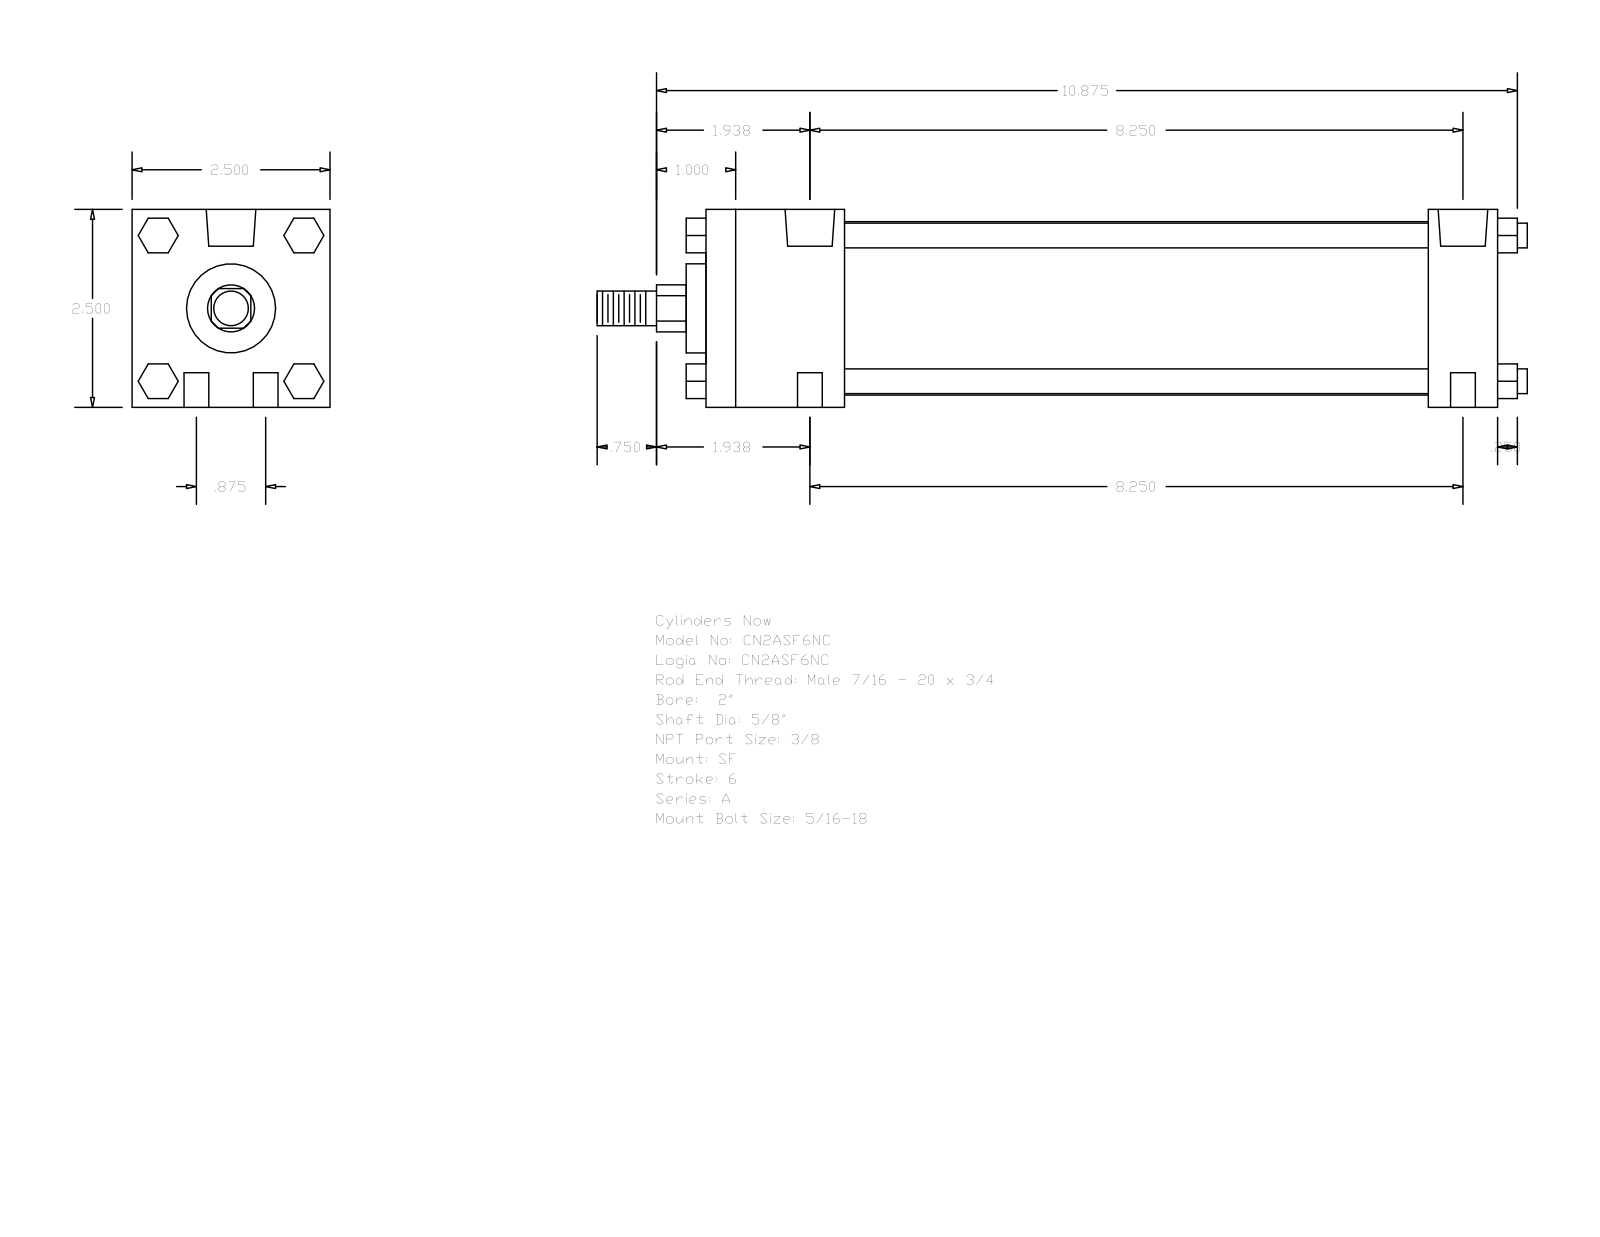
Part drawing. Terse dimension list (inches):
name: A_SF__0200_0.625
written by: GSSL Pune (CONFIG_CONTROL_DESIGN)
unit: in
bodies: 0 solids, 124 faces (94 planar, 30 cylindrical, 0 other)
size: 11.75 × 2.5 × 2.5
holes: 4× ⌀0.313, 2× ⌀0.219, 2× ⌀0.627
bosses: 4× ⌀0.313, 1× ⌀2.19, 1× ⌀1.125, 1× ⌀0.625, 1× ⌀0.437
rounds: 1× R0.297
face distances: 2.5, 10, 9.125, 0.875, 1.75, 7.375, 8.25, 0.25, 10.25, 2
hole spacings: 0.437, 8.261, 8.25, 0.875, 8.296, 7.937
